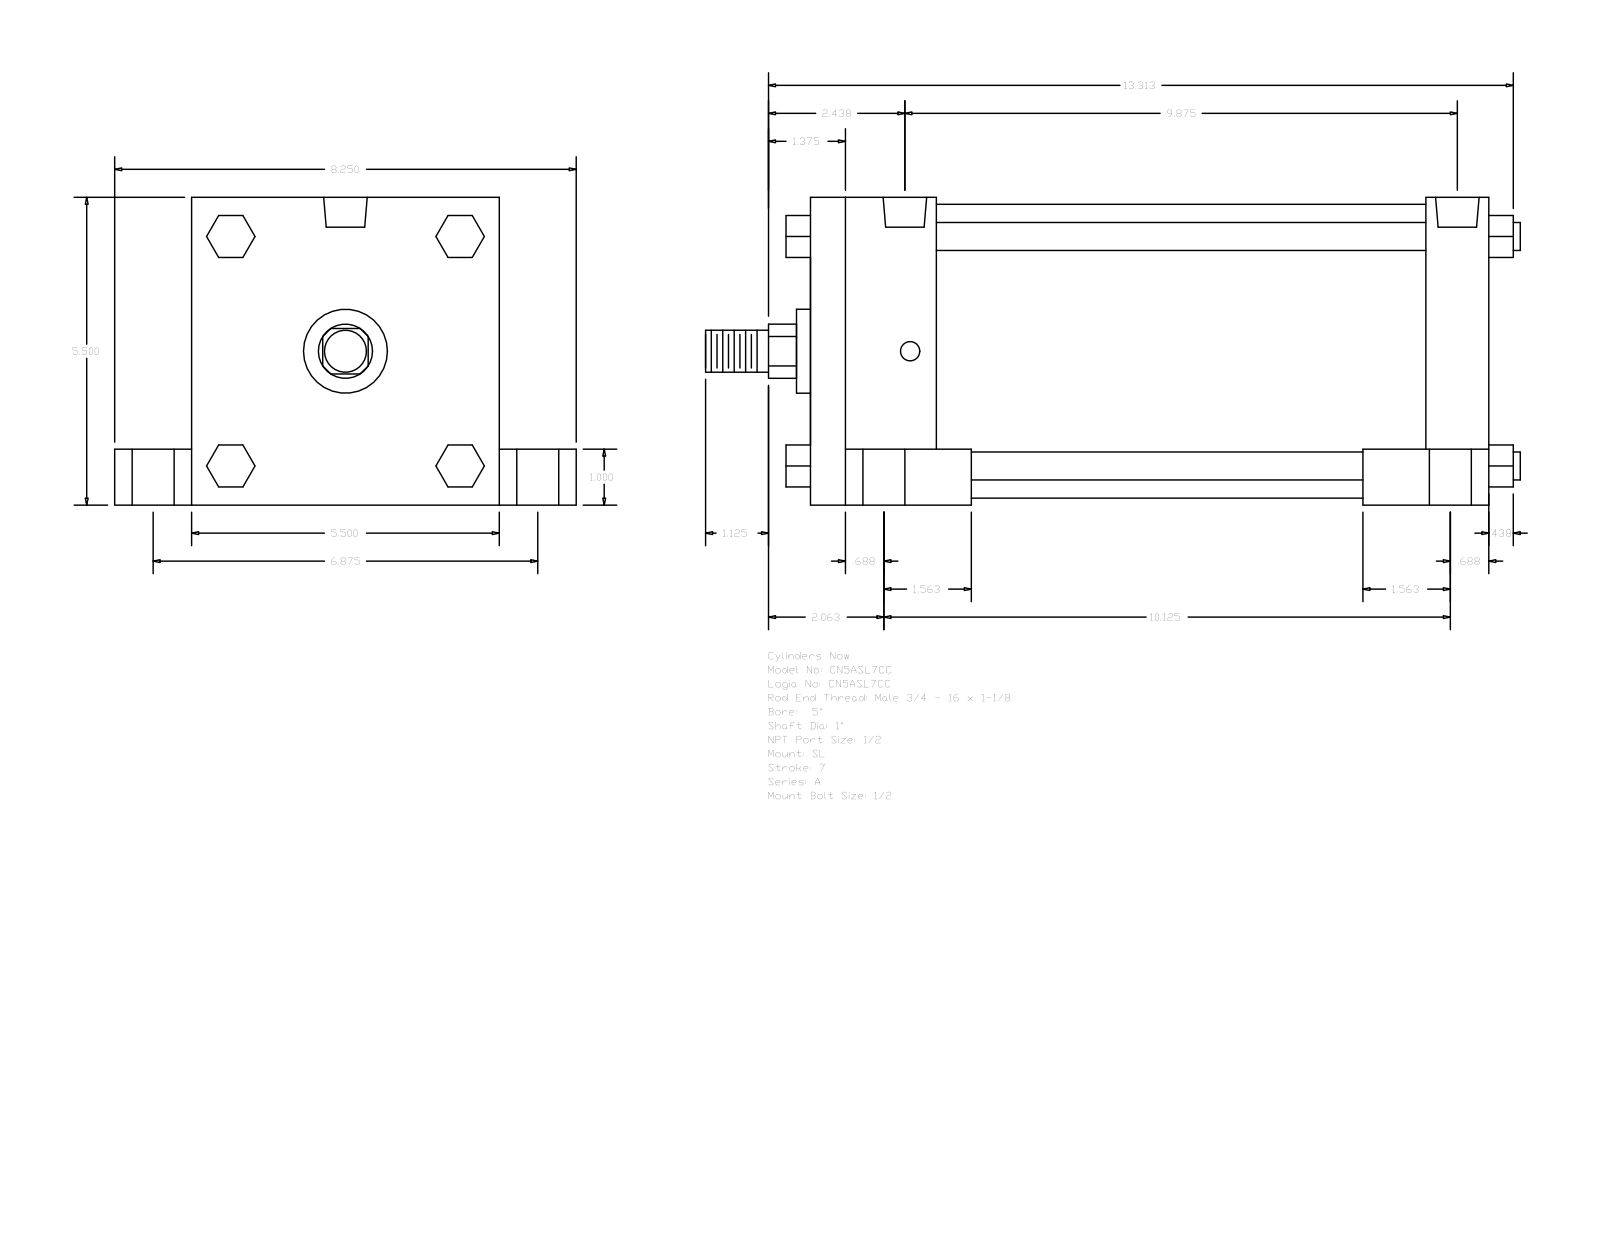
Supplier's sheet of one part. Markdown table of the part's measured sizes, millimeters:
| quantity | value |
| --- | --- |
| part name | A_SL__0500_1 |
| STEP written by | GSSL Pune (CONFIG_CONTROL_DESIGN) |
| units | millimeters |
| bodies | 0 solids, 150 faces (114 planar, 36 cylindrical, 0 other) |
| overall size | 369.89 × 209.55 × 139.7 |
| round holes (diameter × count) | 8.73 × 4, 19.05 × 4, 25.4 × 4, 19.77 × 2 |
| round bosses / shafts (diameter × count) | 12.7 × 4, 133.35 × 1, 38.1 × 1, 25.4 × 1, 19.05 × 1 |
| partial cylindrical surfaces (radius × count) | 12.29 × 1 |
| main face-to-face distances | 139.7, 307.97, 28.57, 25.4, 114.3, 34.93, 174.63, 57.15, 279.4, 222.25 |
| hole center spacings | 2.39, 87.31, 87.37, 87.83, 88.12, 174.62, 246.05, 248.44 |
